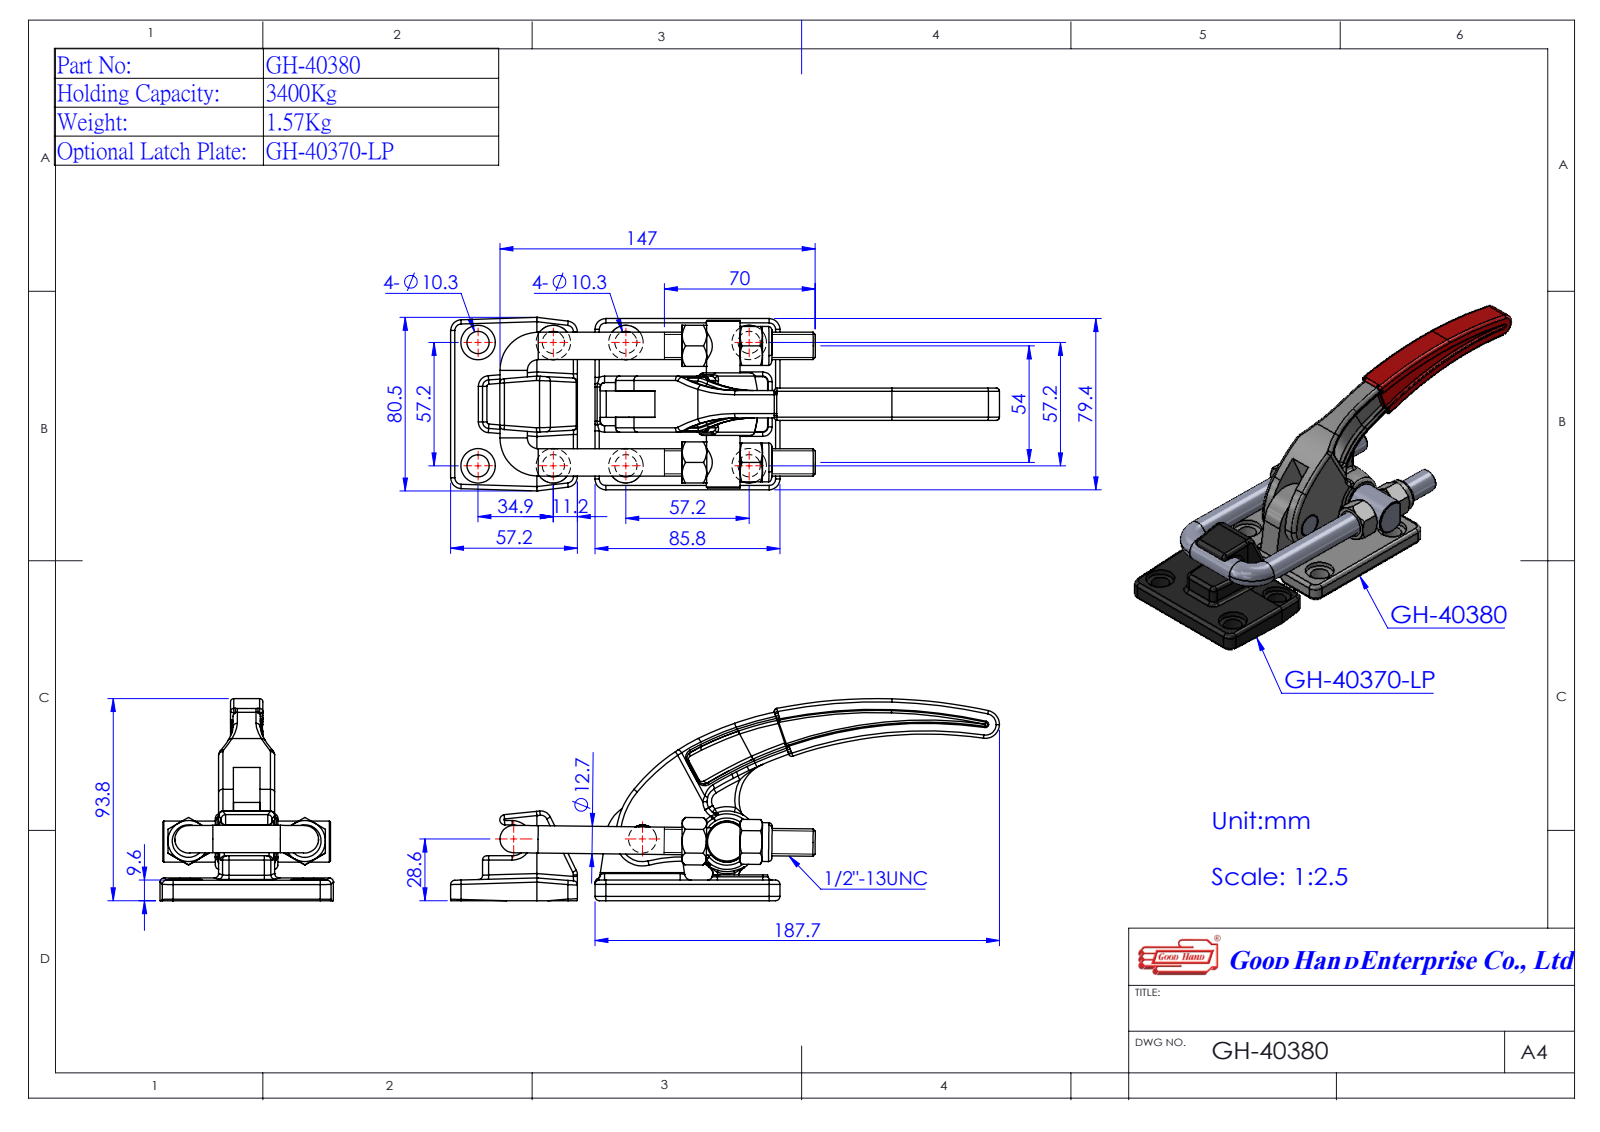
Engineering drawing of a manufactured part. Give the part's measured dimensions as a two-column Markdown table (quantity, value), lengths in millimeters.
| quantity | value |
| --- | --- |
| part name | 44038044-1^GH-40380(簡化)-1; Group1^GH-40380(簡化)-1; Group3^GH-40380(簡化)-1; GH-40380(簡化)-1 (+1 more) |
| STEP written by | SolidWorks 2016 (AUTOMOTIVE_DESIGN) |
| units | millimeters |
| bodies | 6 solids, 355 faces (105 planar, 124 cylindrical, 126 other) |
| overall size | 252.55 × 93.75 × 79.4 |
| volume | 217 306 mm³ |
| surface area | 68 920 mm² |
| round holes (diameter × count) | 10.3 × 4, 16 × 4, 10.2 × 2, 10.72 × 2, 12 × 2, 12.7 × 2, 12.8 × 2, 13.71 × 2, 10 × 1, 19 × 1 |
| round bosses / shafts (diameter × count) | 12.7 × 3, 18 × 2 |
| partial cylindrical surfaces (radius × count) | 2 × 20, 5 × 4, 6.47 × 2, 65.68 × 2, 68.68 × 2, 1 × 1, 6.5 × 1, 12.5 × 1 |
| main face-to-face distances | 9.6, 6.75, 19.25, 20.5, 5.5, 1.25, 13.75, 7, 12.5, 2 |
| hole center spacings | 54, 57.2, 80.89, 39.25 |
